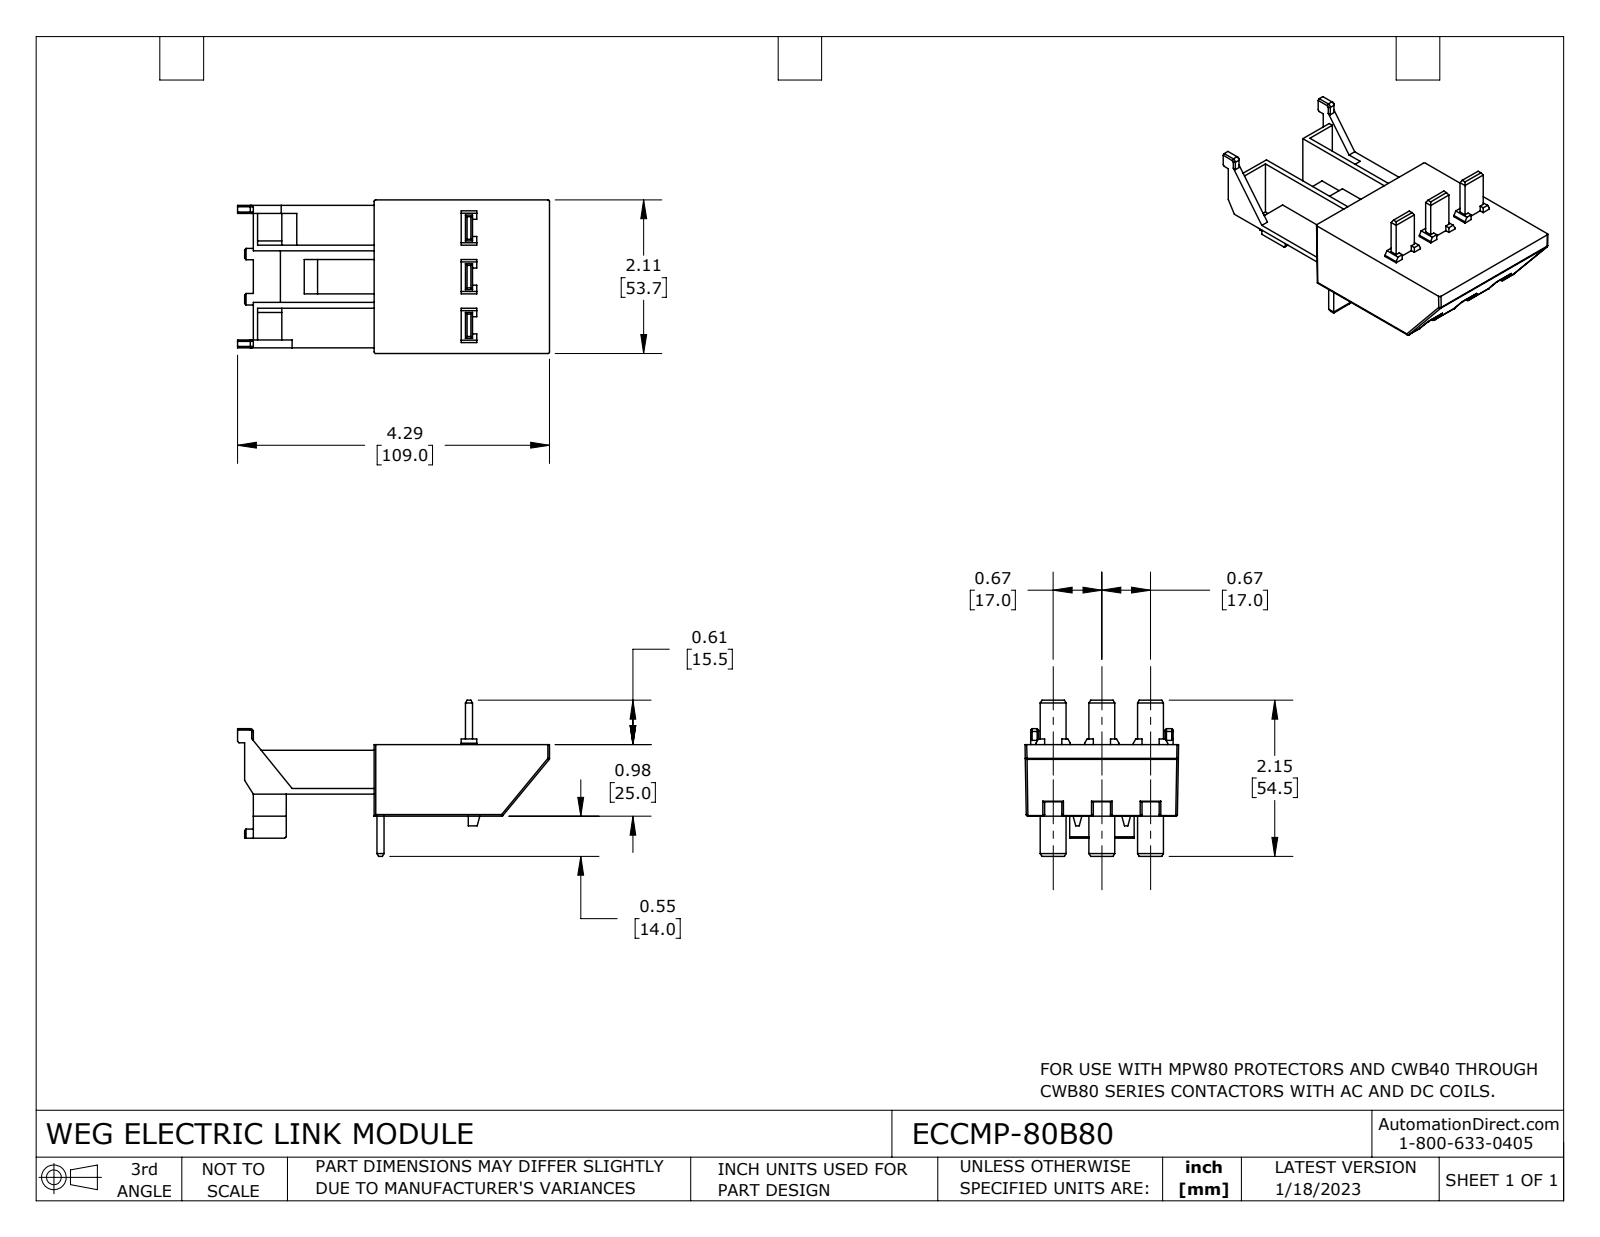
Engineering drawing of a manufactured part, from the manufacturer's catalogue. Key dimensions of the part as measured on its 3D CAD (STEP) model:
Part name (STEP PRODUCT): ECCMP-80B80
STEP written by: SolidWorks 2021 (CONFIG_CONTROL_DESIGN)
Units: millimetres
Bodies: 2 solids, 278 faces (225 planar, 33 cylindrical, 20 other)
Overall size (bounding box): 109 × 54.5 × 53.65
Volume: 68 377 mm³ · Surface area: 27 181 mm²
Partial cylindrical surfaces — rounded edges, fillets, slot ends (radius × count): R0.6 ×23, R1 ×1, R5 ×1
Main face-to-face distances: 2, 13.25, 1.5, 34.4, 17.3, 4.05, 20, 14.4, 75.1, 3
